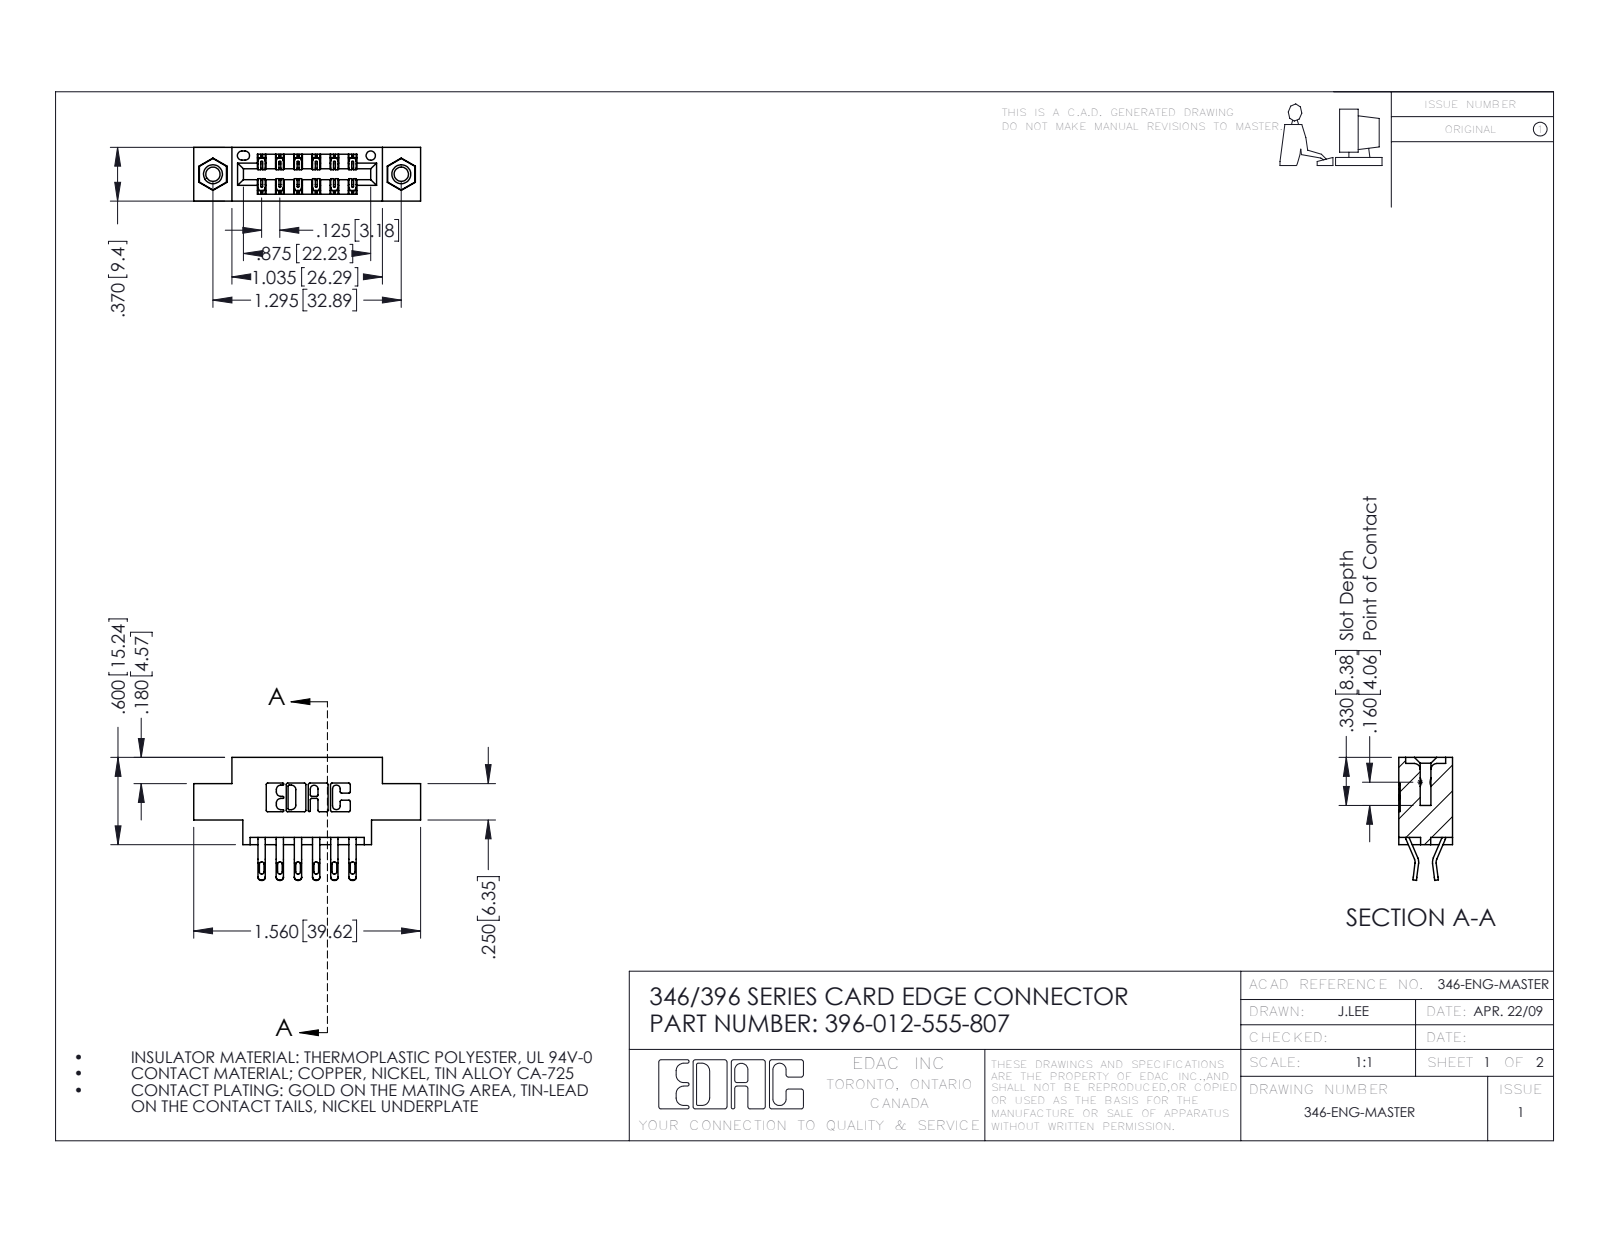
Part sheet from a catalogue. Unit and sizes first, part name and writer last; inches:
Units: inches
Overall size (bounding box): 1.56 × 0.845 × 0.37
Round holes (diameter × count): ⌀0.098 ×2, ⌀0.125 ×2, ⌀0.156 ×2, ⌀0.064 ×1
Round bosses / shafts (diameter × count): ⌀0.155 ×2
Partial cylindrical surfaces — rounded edges, fillets, slot ends (radius × count): R0.016 ×24, R0.02 ×24, R0.01 ×22, R0.006 ×18, R0.007 ×6, R0.031 ×6, R0.026 ×3, R0.01 ×2
Main face-to-face distances: 0.25, 0.37, 0.048, 0.322, 0.222, 0.148, 0.1, 0.174, 0.025, 0.072
Hole centre spacings: 0.246, 1.092, 1.295
Volume: 0.211 in³ · Surface area: 6.998 in²
Bodies: 15 solids, 882 faces (508 planar, 358 cylindrical, 16 other)
Part name (STEP PRODUCT): 345-292-001_555 Tail; 346 Part_0.170 Offset - 0.156 Dia-TI; 345-250-001_345-250-005-103; 396-012-555-807
STEP written by: SolidWorks 2016 (CONFIG_CONTROL_DESIGN)
